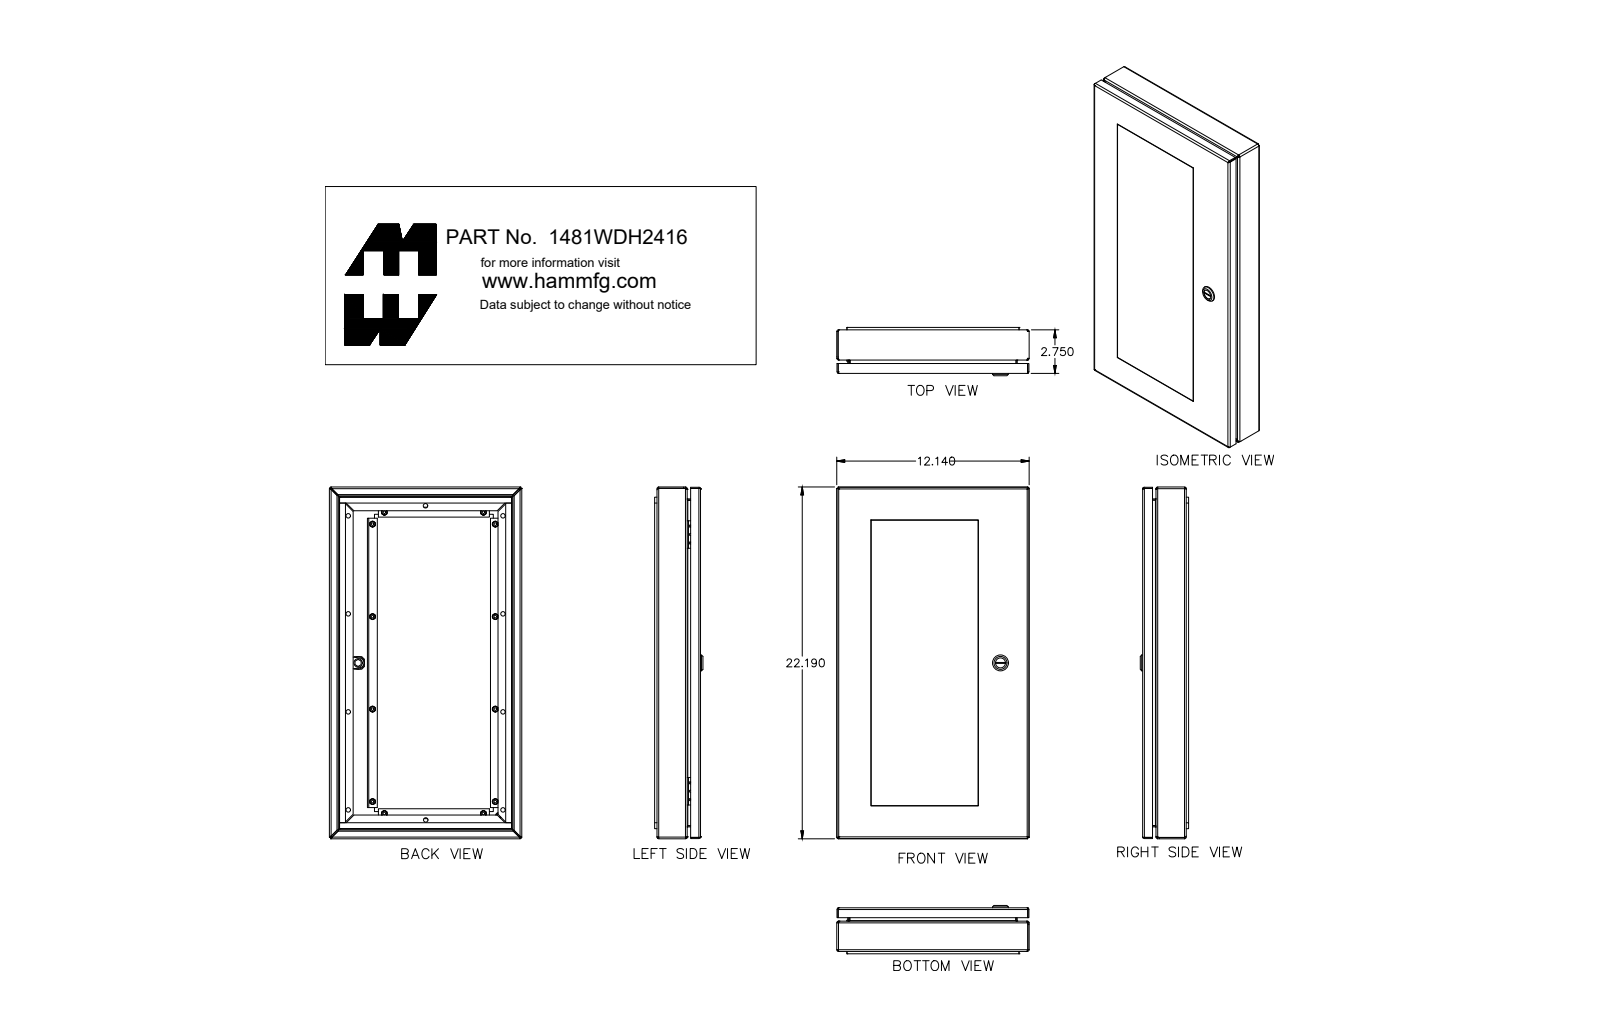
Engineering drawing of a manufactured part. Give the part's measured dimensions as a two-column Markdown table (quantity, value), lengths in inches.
| quantity | value |
| --- | --- |
| part name | 1481WDH2416_Default |
| STEP written by | SolidWorks 2019 (CONFIG_CONTROL_DESIGN) |
| units | inches |
| bodies | 45 solids, 1062 faces (569 planar, 301 cylindrical, 192 other) |
| overall size | 22.19 × 12.14 × 2.91 |
| volume | 71.6 in³ |
| surface area | 1 412 in² |
| round holes (diameter × count) | 0.13 × 12, 0.281 × 10, 0.136 × 2, 0.232 × 1, 0.24 × 1, 0.242 × 1, 0.625 × 1, 0.785 × 1 |
| round bosses / shafts (diameter × count) | 0.368 × 12, 0.226 × 12, 0.164 × 12, 1.1 × 1, 0.525 × 1, 0.455 × 1, 0.398 × 1, 0.356 × 1 |
| partial cylindrical surfaces (radius × count) | 0.036 × 28, 0.108 × 28, 0.101 × 24, 0.016 × 4, 0.088 × 4, 0.125 × 2, 0.021 × 1, 0.029 × 1 |
| main face-to-face distances | 0.072, 0.25, 0.178, 2.578, 0.842, 1.736, 2.328, 12.068, 0.592, 2.65 |
| hole center spacings | 9.7, 11.556, 4.923, 5.833, 6.182, 7.04, 7.75, 9.764 |
